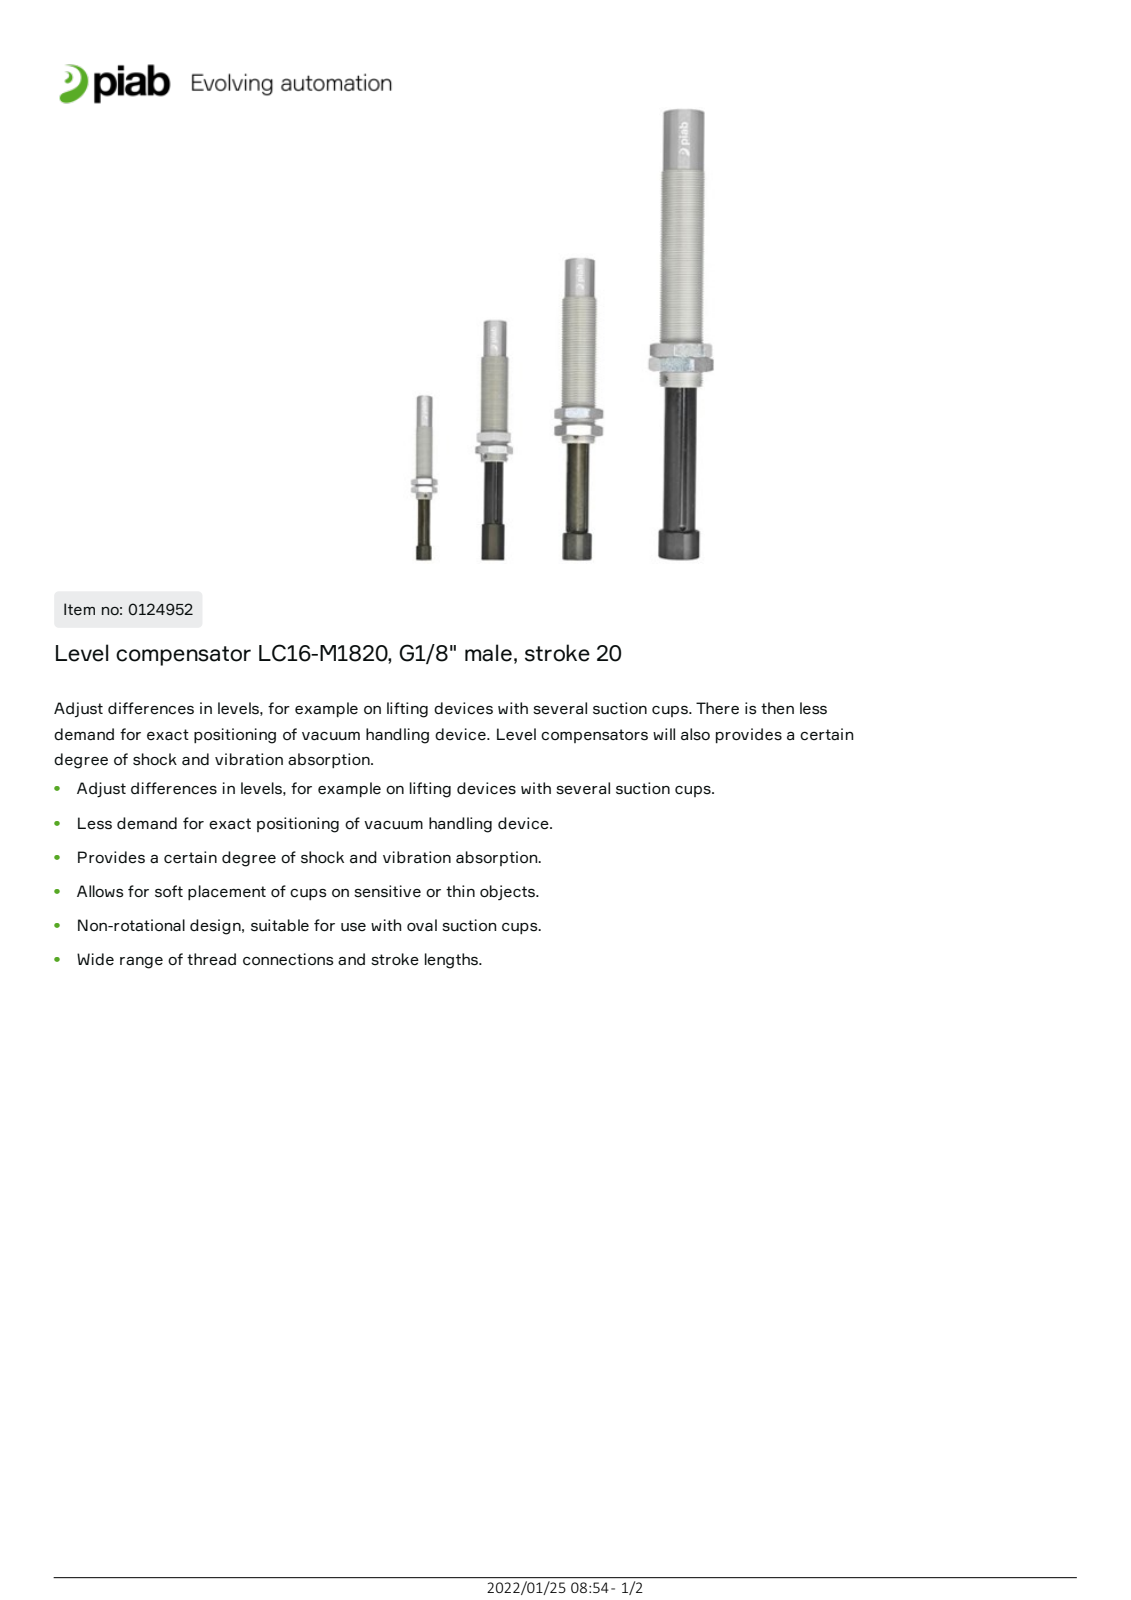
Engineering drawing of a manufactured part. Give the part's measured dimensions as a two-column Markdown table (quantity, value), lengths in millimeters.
| quantity | value |
| --- | --- |
| part name | NutM16x1; Adaptor Nut G18; Body threaded; Rod vacuum (+1 more) |
| STEP written by | Unknown (automotive_design) |
| units | millimeters |
| bodies | 11 solids, 159 faces (74 planar, 49 cylindrical, 36 other) |
| overall size | 98.5 × 30.97 × 21.94 |
| volume | 24 531 mm³ |
| surface area | 21 388 mm² |
| round holes (diameter × count) | 6 × 2, 8.7 × 2, 15 × 2, 4.2 × 1, 10.7 × 1 |
| round bosses / shafts (diameter × count) | 9.5 × 2, 16 × 1, 8 × 1 |
| partial cylindrical surfaces (radius × count) | 6.4 × 2 |
| main face-to-face distances | 12, 3.5, 15.5, 5, 6, 19, 7, 31.5, 1, 11 |
